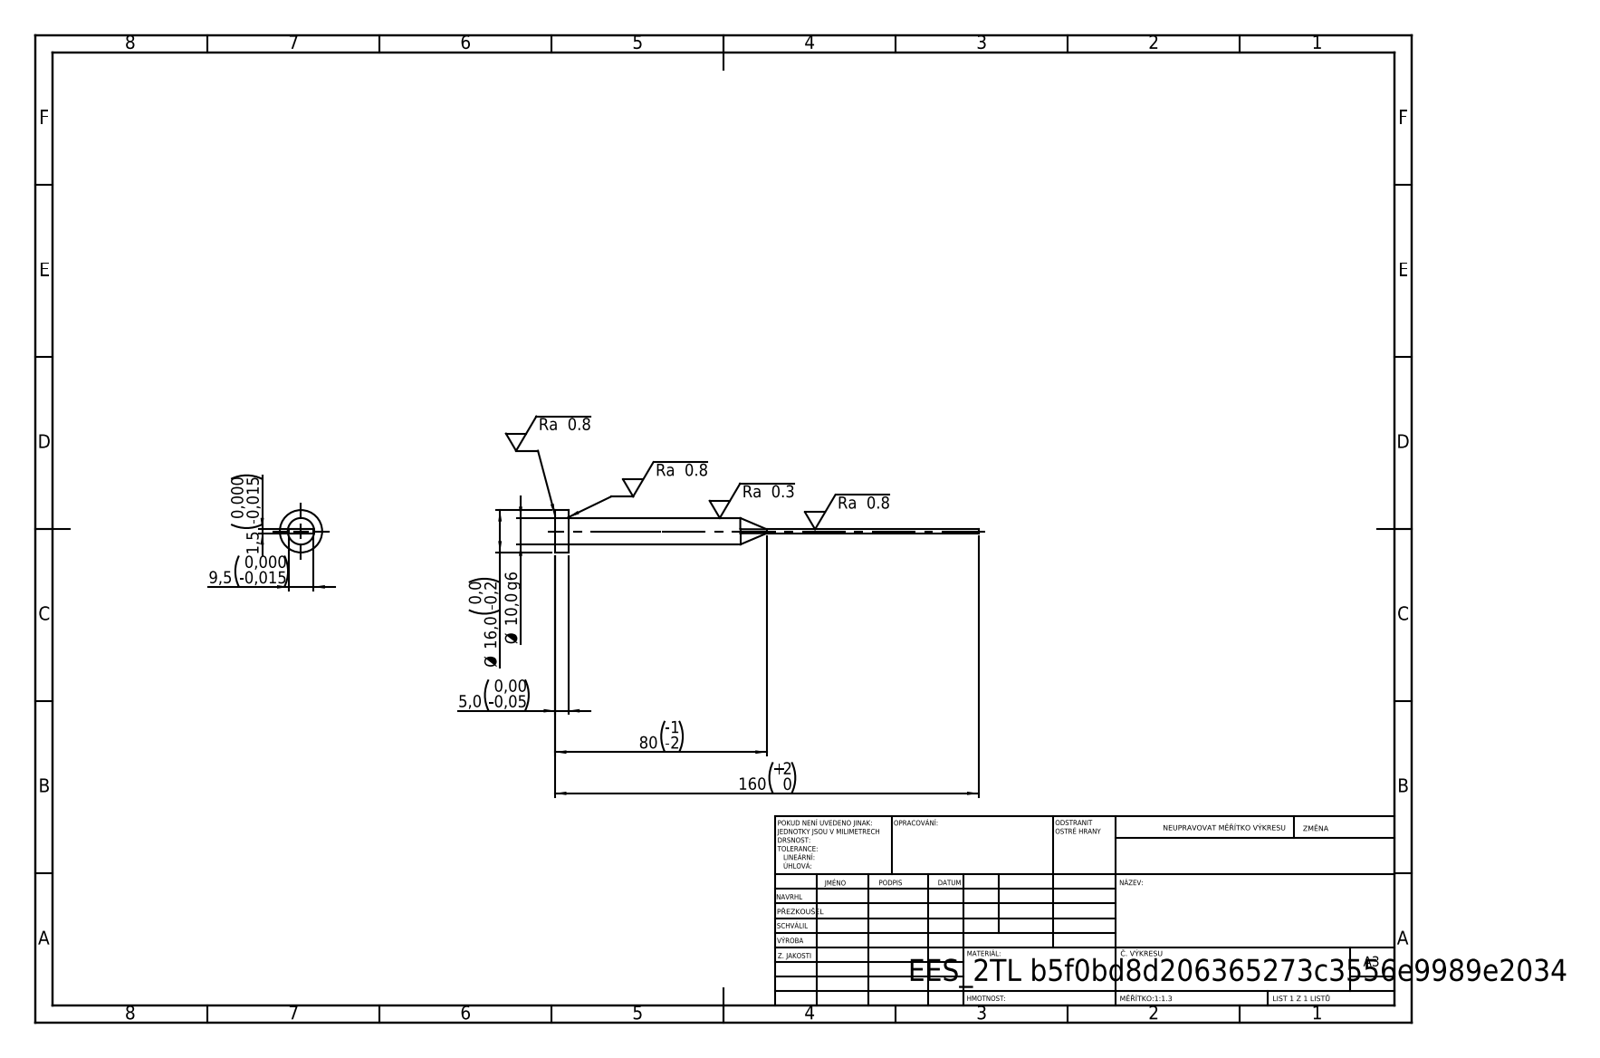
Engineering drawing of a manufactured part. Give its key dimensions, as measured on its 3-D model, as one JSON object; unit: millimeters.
{"step_written_by": "SolidWorks 2019 (CONFIG_CONTROL_DESIGN)", "units": "millimeters", "bodies": {"solids": 1, "faces": 15, "planar": 7, "cylindrical": 4, "other": 4}, "overall_size": [160, 16, 16], "volume_mm3": 7688, "surface_area_mm2": 4656, "round_bosses_or_shafts": [[16, 1], [10, 1]], "face_to_face_distances": [1.5, 5, 9.5, 160, 155]}
